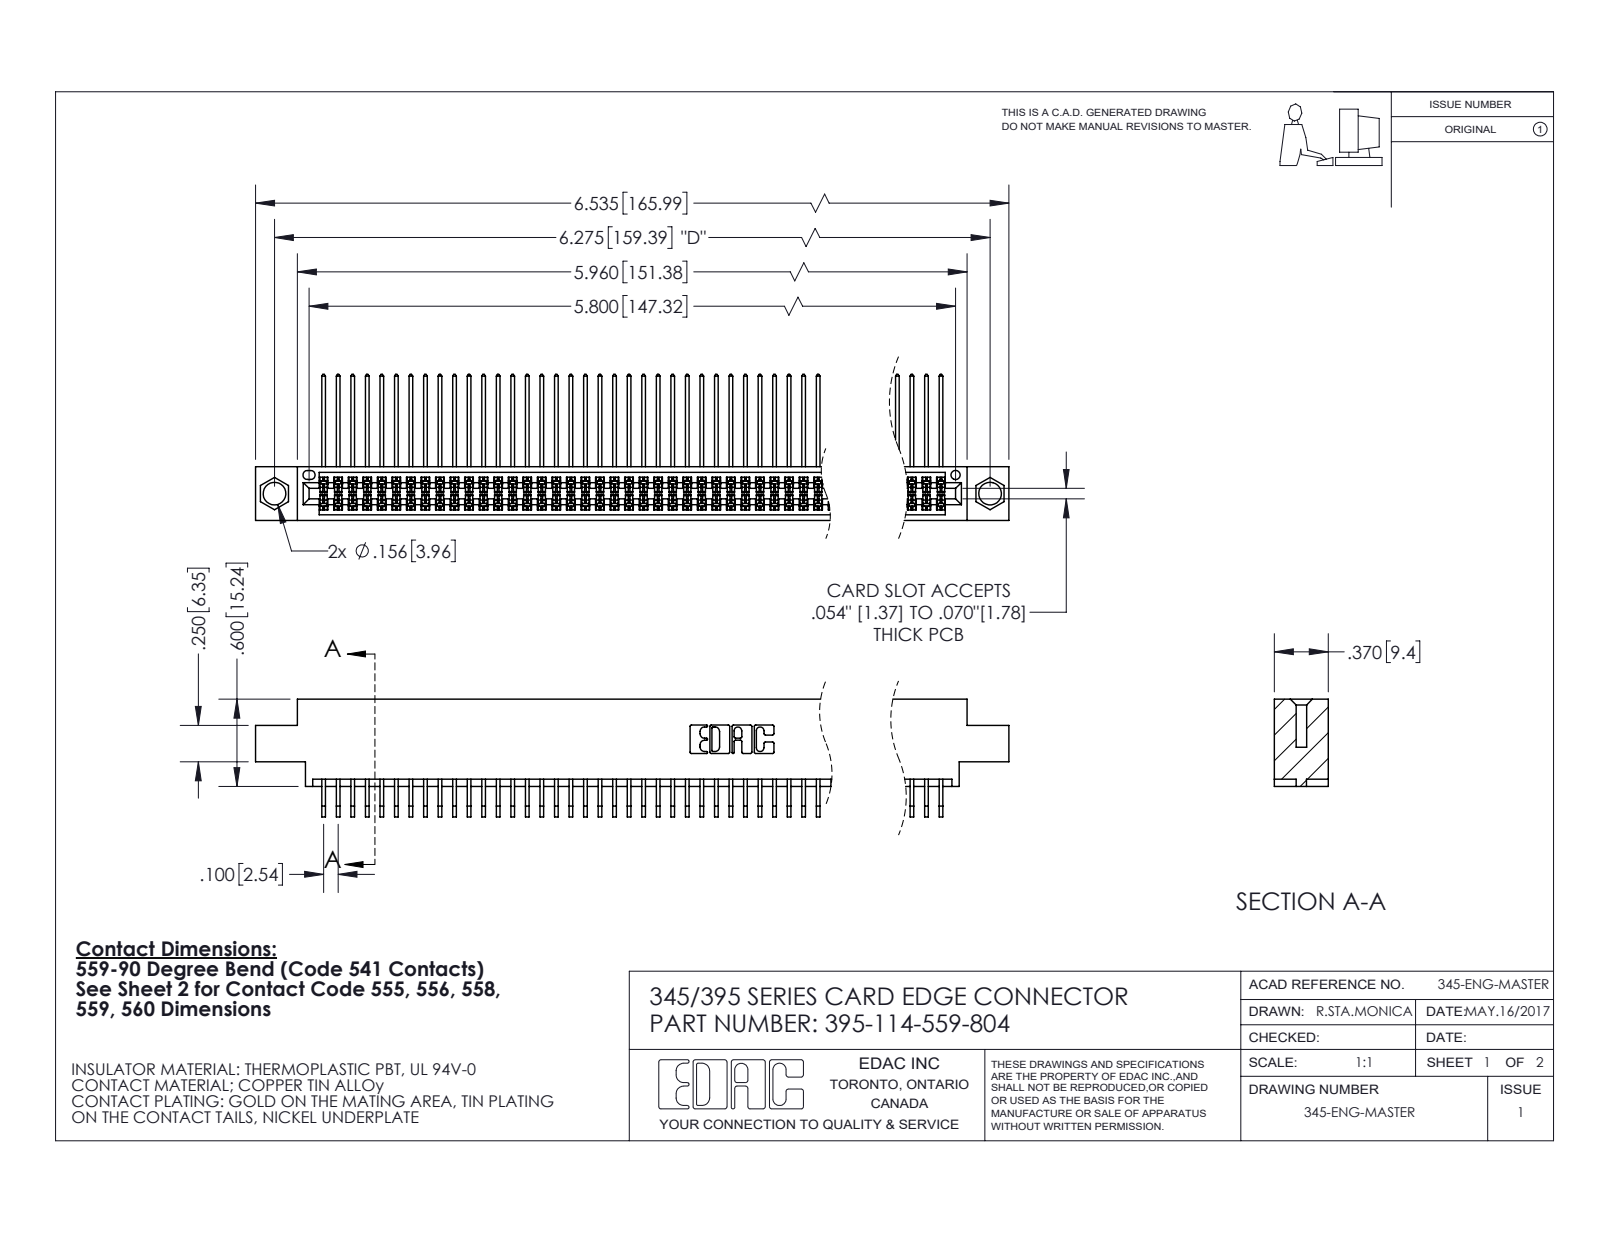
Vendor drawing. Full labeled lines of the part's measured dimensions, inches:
Part name (STEP PRODUCT): 345-292-001_559 Tail - 2; 345-292-001_558 559 Tail - 1; 395-114-559-804; 345 Part_0.170 Offset - 0.156 Dia-TI
STEP written by: SolidWorks 2020 (CONFIG_CONTROL_DESIGN)
Units: inches
Bodies: 115 solids, 6072 faces (4088 planar, 1984 cylindrical, 0 other)
Overall size (bounding box): 6.535 × 1.005 × 0.809
Volume: 1.019 in³ · Surface area: 43.5 in²
Round holes (diameter × count): ⌀0.156 ×2, ⌀0.064 ×1
Partial cylindrical surfaces — rounded edges, fillets, slot ends (radius × count): R0.006 ×227, R0.01 ×22, R0.007 ×6, R0.031 ×6, R0.026 ×3, R0.014 ×2, R0.019 ×2, R0.022 ×2
Main face-to-face distances: 0.072, 0.298, 0.37, 0.2, 0.098, 0.272, 0.025, 0.225, 0.175, 0.15
Hole centre spacings: 0.27, 6.039, 6.275
